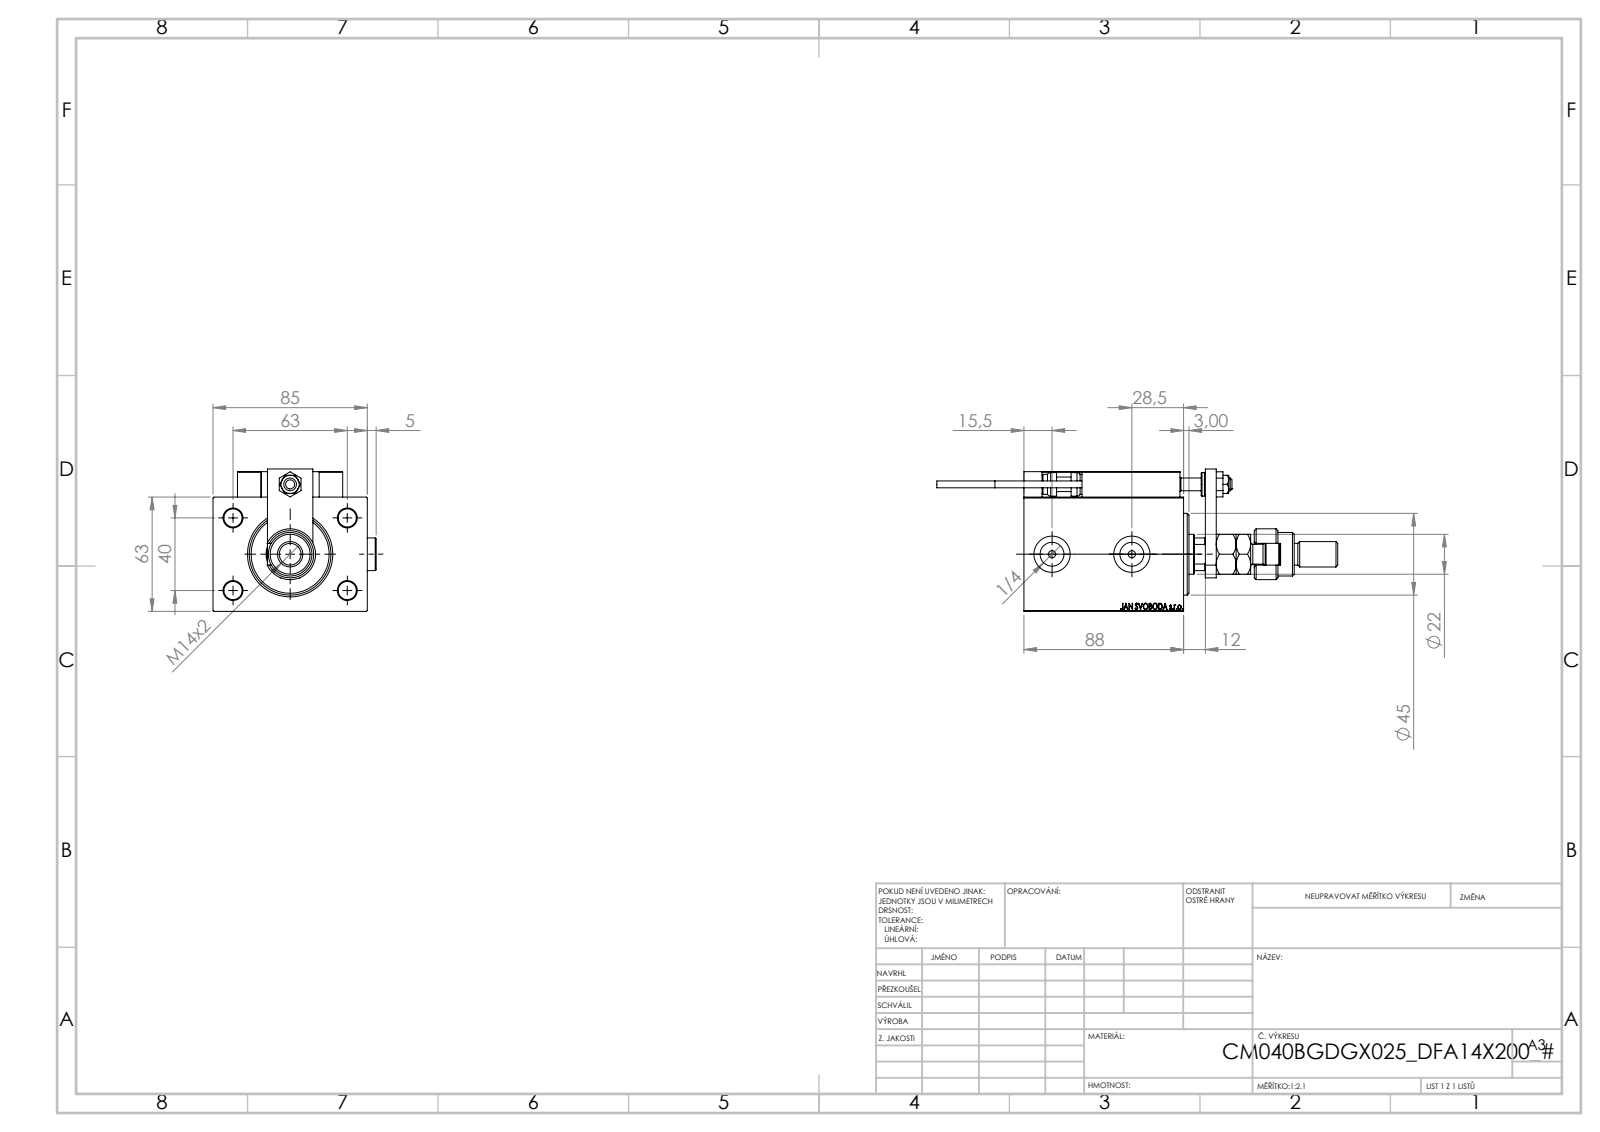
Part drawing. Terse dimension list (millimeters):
name: SWITCH X; NUT_D10; TYC_L79; SWITCH_X_FRONT_BACK (+7 more)
written by: SolidWorks 2019 (CONFIG_CONTROL_DESIGN)
unit: mm
bodies: 28 solids, 1457 faces (623 planar, 213 cylindrical, 621 other)
size: 221 × 89.9 × 78.5
volume: 506 329 mm³; area: 105 513 mm²
holes: 6× ⌀4, 5× ⌀8, 4× ⌀3.2, 4× ⌀10, 2× ⌀5, 2× ⌀13.16, 2× ⌀20, 1× ⌀7, 1× ⌀12.5, 1× ⌀16.5, 1× ⌀22, 1× ⌀25.5
bosses: 3× ⌀18, 2× ⌀11, 2× ⌀5, 2× ⌀3.8, 1× ⌀28, 1× ⌀24, 1× ⌀14, 1× ⌀13
rounds: 30× R0.3, 2× R3, 1× R9.75, 1× R10.5
face distances: 63, 12, 76, 85, 88, 14, 25, 30, 18, 77
hole spacings: 37.31, 11.37, 20, 29.59, 29.69, 36.06, 36.53, 40
